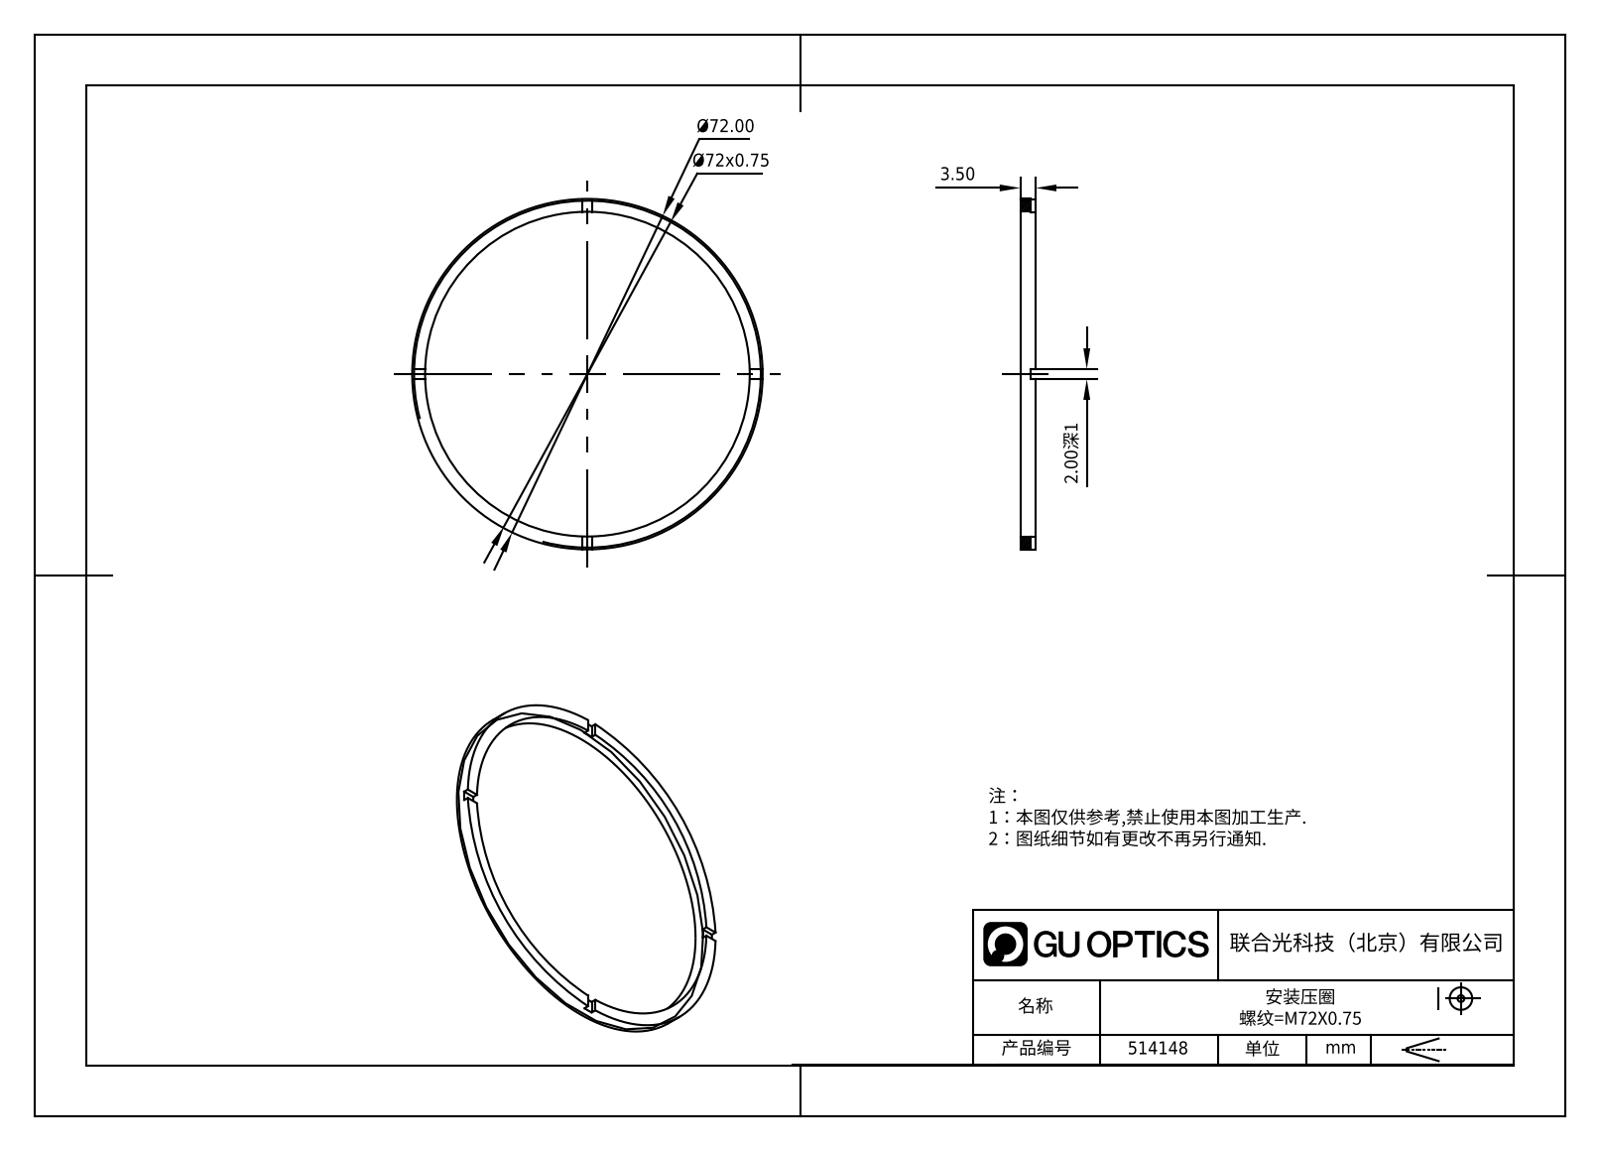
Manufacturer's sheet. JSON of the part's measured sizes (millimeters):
{"part_name": "514148", "step_written_by": "SolidWorks 2020 (CONFIG_CONTROL_DESIGN)", "units": "millimeters", "bodies": {"solids": 1, "faces": 21, "planar": 17, "cylindrical": 4, "other": 0}, "overall_size": [72, 72, 3.5], "volume_mm3": 2252, "surface_area_mm2": 2826, "round_holes": [[66, 1]], "round_bosses_or_shafts": [[72, 1]], "face_to_face_distances": [3.5, 2.5, 1, 2]}
